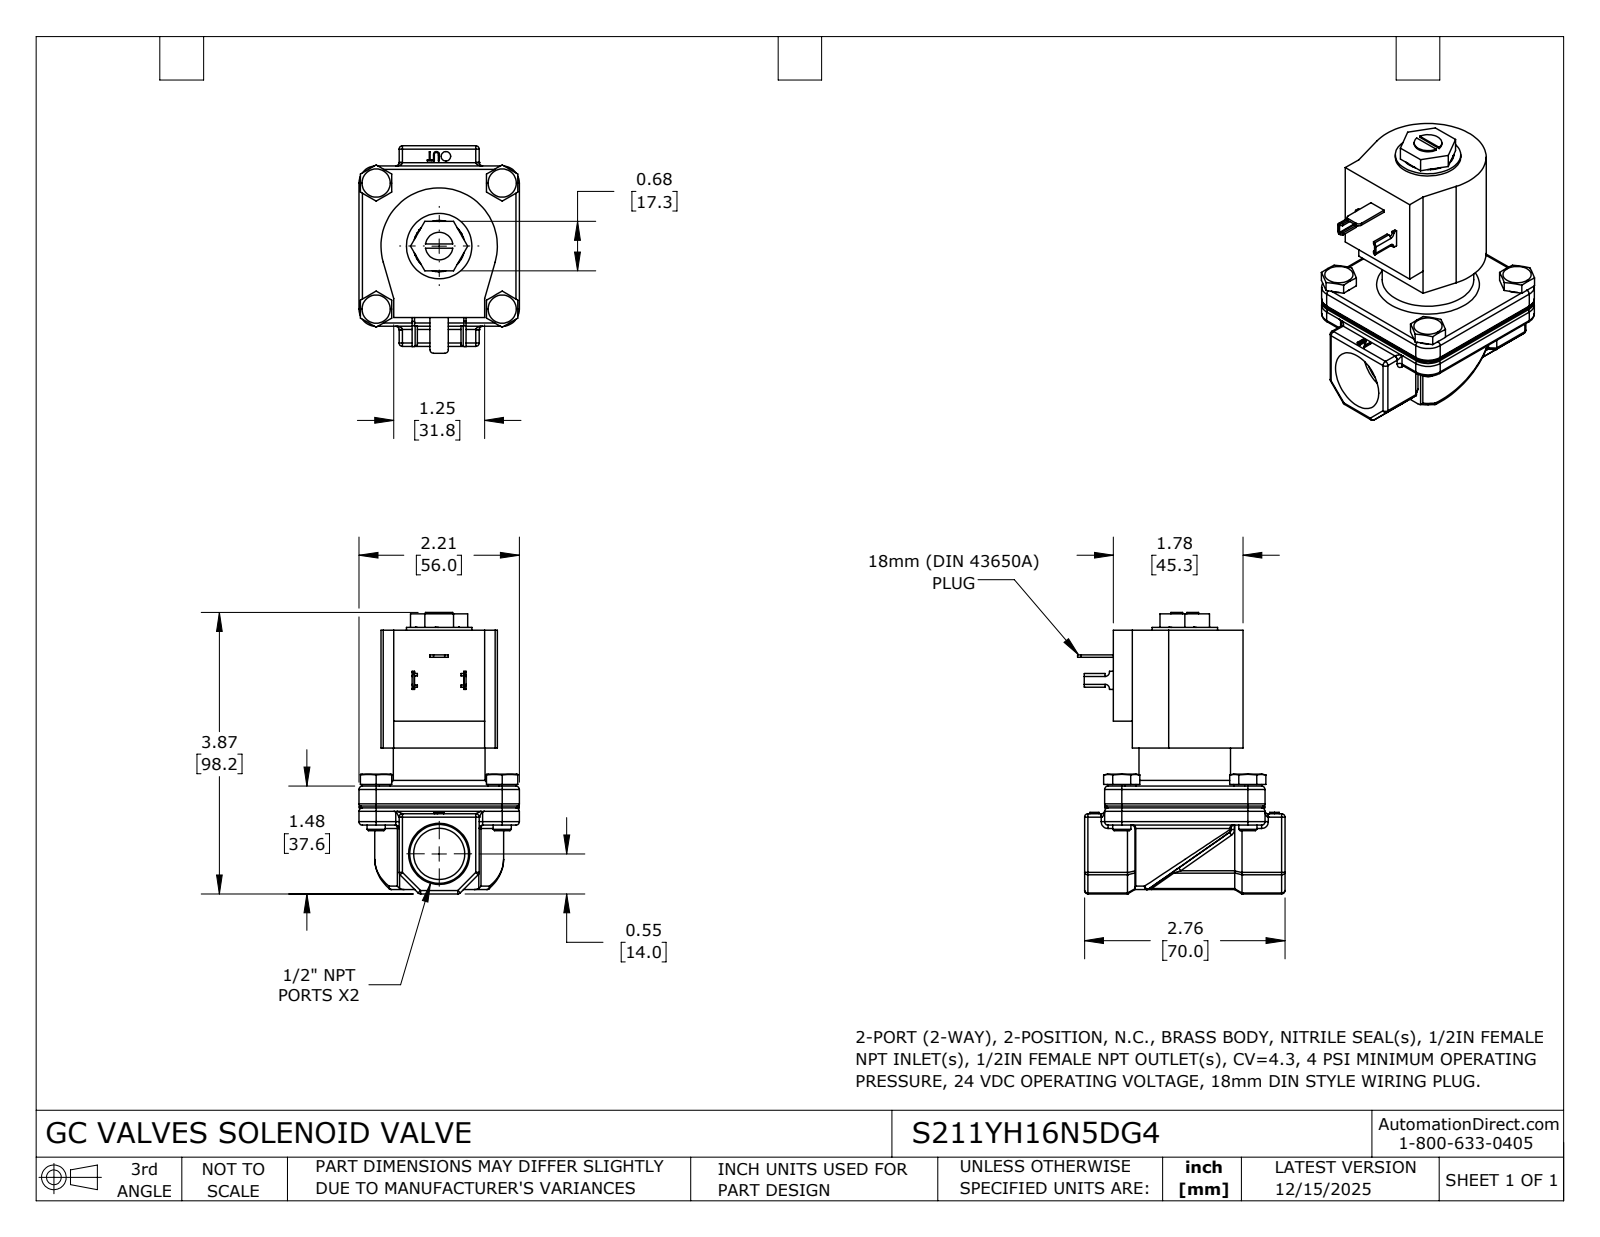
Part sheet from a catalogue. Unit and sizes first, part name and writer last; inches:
Units: inches
Overall size (bounding box): 3.867 × 2.851 × 2.205
Round holes (diameter × count): ⌀0.703 ×1, ⌀0.706 ×1
Round bosses / shafts (diameter × count): ⌀0.388 ×4, ⌀0.25 ×4, ⌀1.26 ×1, ⌀0.9 ×1, ⌀0.464 ×1, ⌀0.38 ×1
Partial cylindrical surfaces — rounded edges, fillets, slot ends (radius × count): R0.047 ×64, R0.006 ×4, R0.031 ×4, R0.041 ×4, R0.234 ×4, R0.236 ×4, R0.05 ×2, R0.06 ×2
Main face-to-face distances: 2.143, 0.059, 0.551, 1.654, 0.537, 2.68, 2.205, 1.06, 0.523, 1.62
Volume: 9.426 in³ · Surface area: 42.83 in²
Bodies: 1 solid, 507 faces (201 planar, 158 cylindrical, 148 other)
Part name (STEP PRODUCT): S211YH16N5DG4
STEP written by: SolidWorks 2024 (CONFIG_CONTROL_DESIGN)
